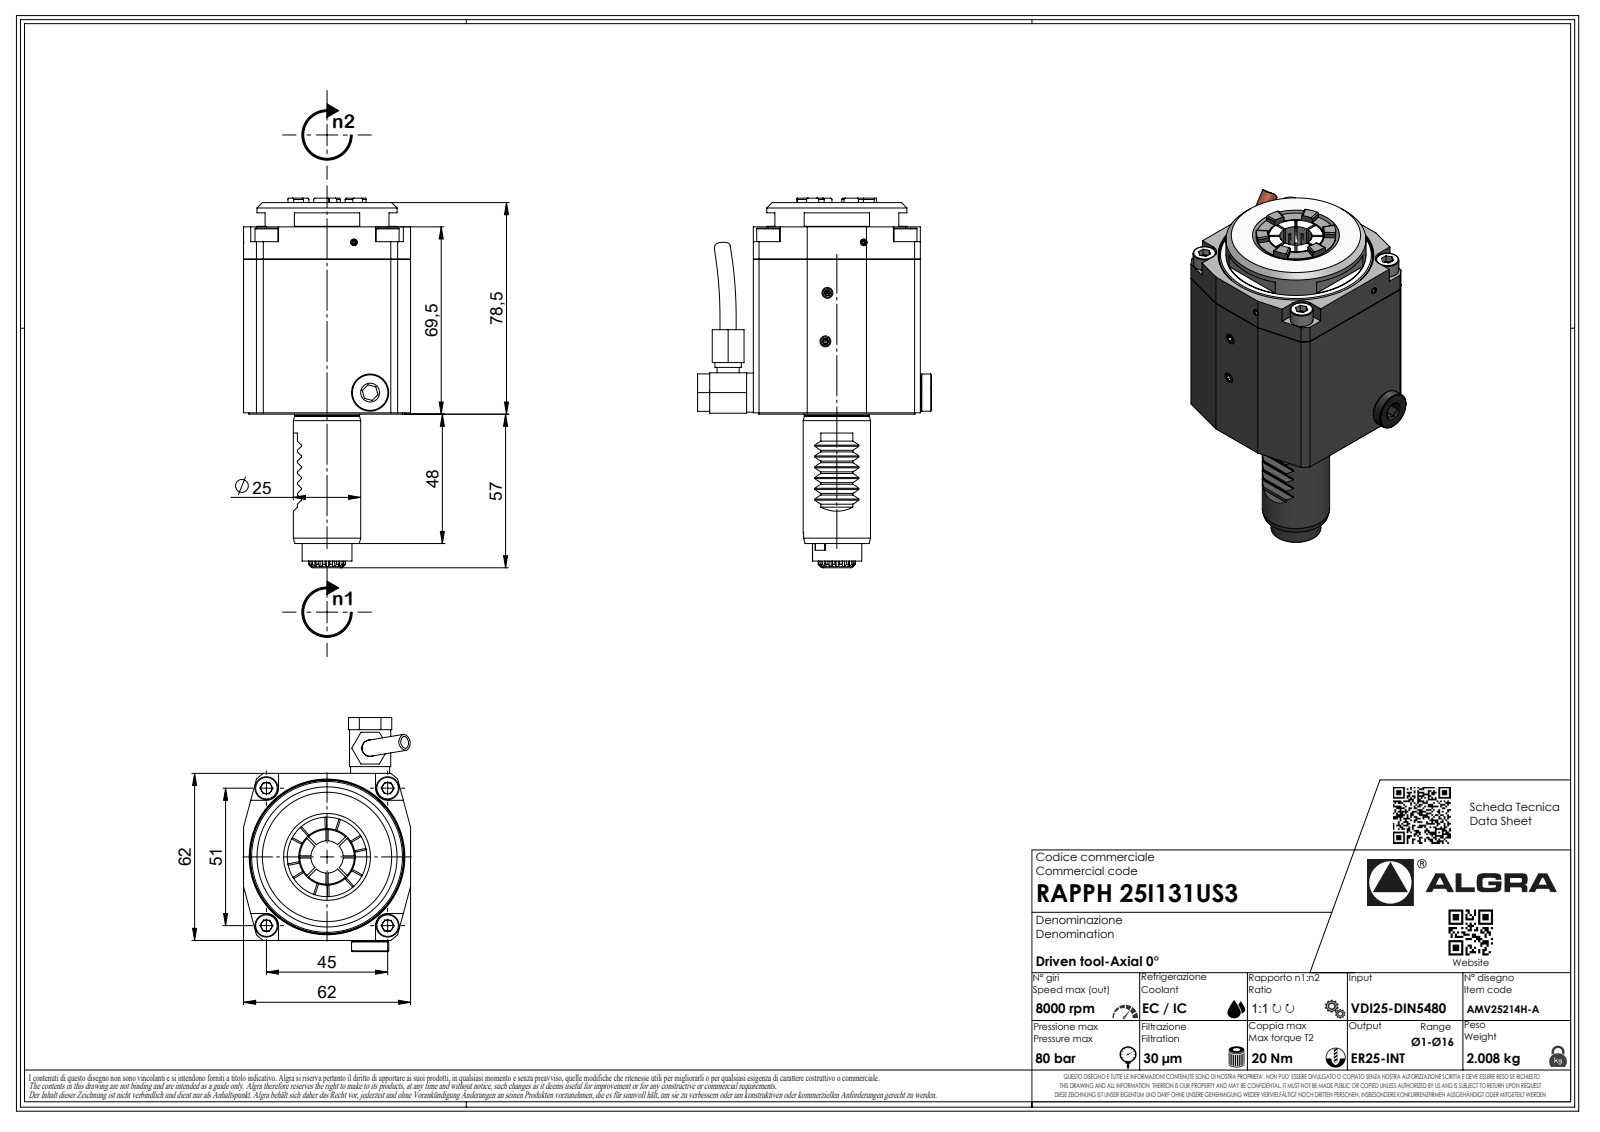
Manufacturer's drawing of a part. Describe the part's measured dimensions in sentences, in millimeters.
The part is named "RAPPH25I131US3". Its 3-D file was written by "SolidWorks 2023 (AUTOMOTIVE_DESIGN)". It is 1 solid with 711 faces: 424 planar, 135 cylindrical and 152 other. Overall it measures 137.15 by 86.85 by 62 millimeters. Its volume is 297 498 cubic millimeters and its surface area 35 100 square millimeters. Round holes: 1 of diameter 2.1, 1 of diameter 18.7, 1 of diameter 22. Round bosses or shafts: 1 of diameter 58, 1 of diameter 52, 1 of diameter 25, 1 of diameter 24.1, 1 of diameter 18.5, 1 of diameter 14.5, 1 of diameter 13.8, 1 of diameter 12. Partial cylindrical surfaces (rounded edges, fillets, slot ends): 8 of radius 35, 7 of radius 0.33, 7 of radius 0.52, 7 of radius 3.7, 6 of radius 0.3, 4 of radius 4.5, 1 of radius 0.21, 1 of radius 3.25. The main face-to-face distances are 62, 65.58, 78.5, 9, 69.5, 0.5, 69, 78, 65.59, 8.
